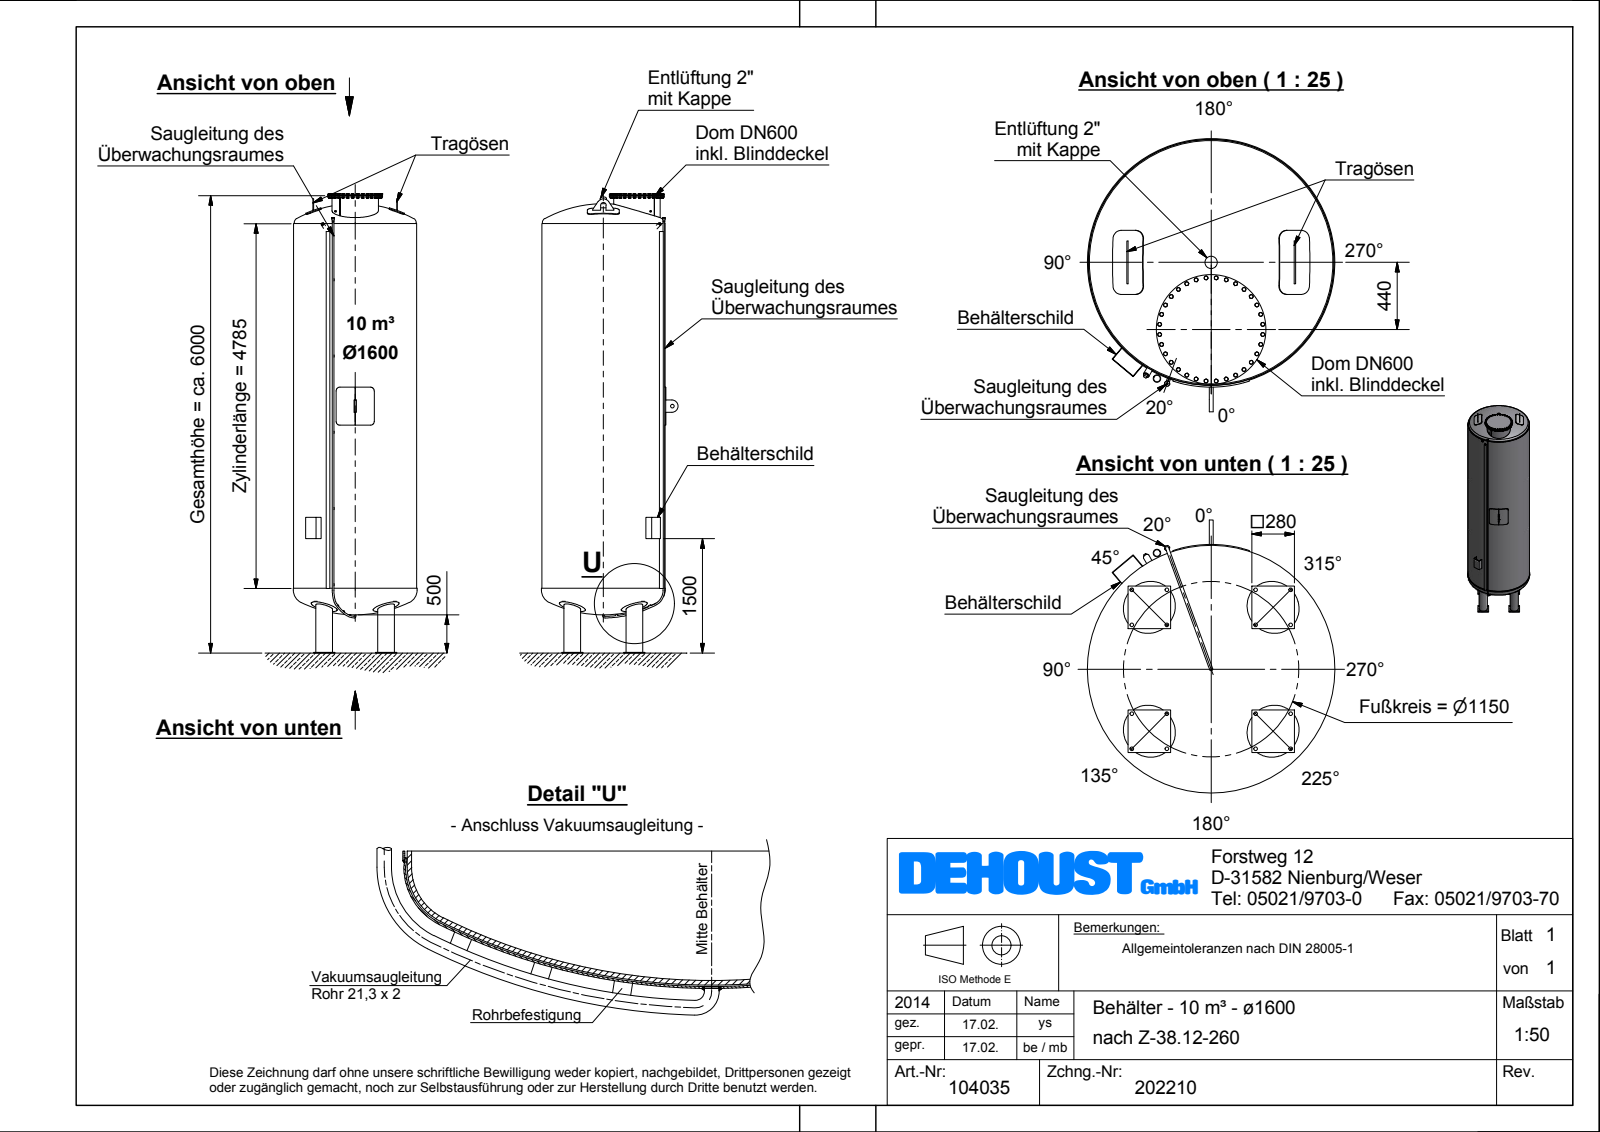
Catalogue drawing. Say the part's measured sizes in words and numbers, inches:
The part is named "Z-38_12-260_Beh\\S\\dlter_\\S\\x1600_010m\\S\\3_Dichte=1,0". Its 3-D file was written by "Autodesk Inventor 2012 (AUTOMOTIVE_DESIGN)". It is 9 solids with 1163 faces: 689 planar, 150 cylindrical and 324 other. Overall it measures 237.376 by 67.731 by 63.937 inches. Its volume is 632 800 cubic inches and its surface area 63 240 square inches. Round holes: 4 of diameter 8.232, 1 of diameter 23.543, 1 of diameter 62.598. Round bosses or shafts: 32 of diameter 0.886, 32 of diameter 0.63, 4 of diameter 13.78, 4 of diameter 8.626, 2 of diameter 0.839, 1 of diameter 63.937, 1 of diameter 63.622, 1 of diameter 62.992. Partial cylindrical surfaces (rounded edges, fillets, slot ends): 8 of radius 2.205, 4 of radius 1.969, 2 of radius 1.378, 2 of radius 3.346, 1 of radius 3.15, 1 of radius 32.205. The main face-to-face distances are 15.122, 13.744, 1.378, 236.982, 0.394, 221.86, 235.604, 221.467, 235.21, 236.588. The hole center spacings are 22.638, 32.015, 16.061, 36.975, 45.276, 17.323.
